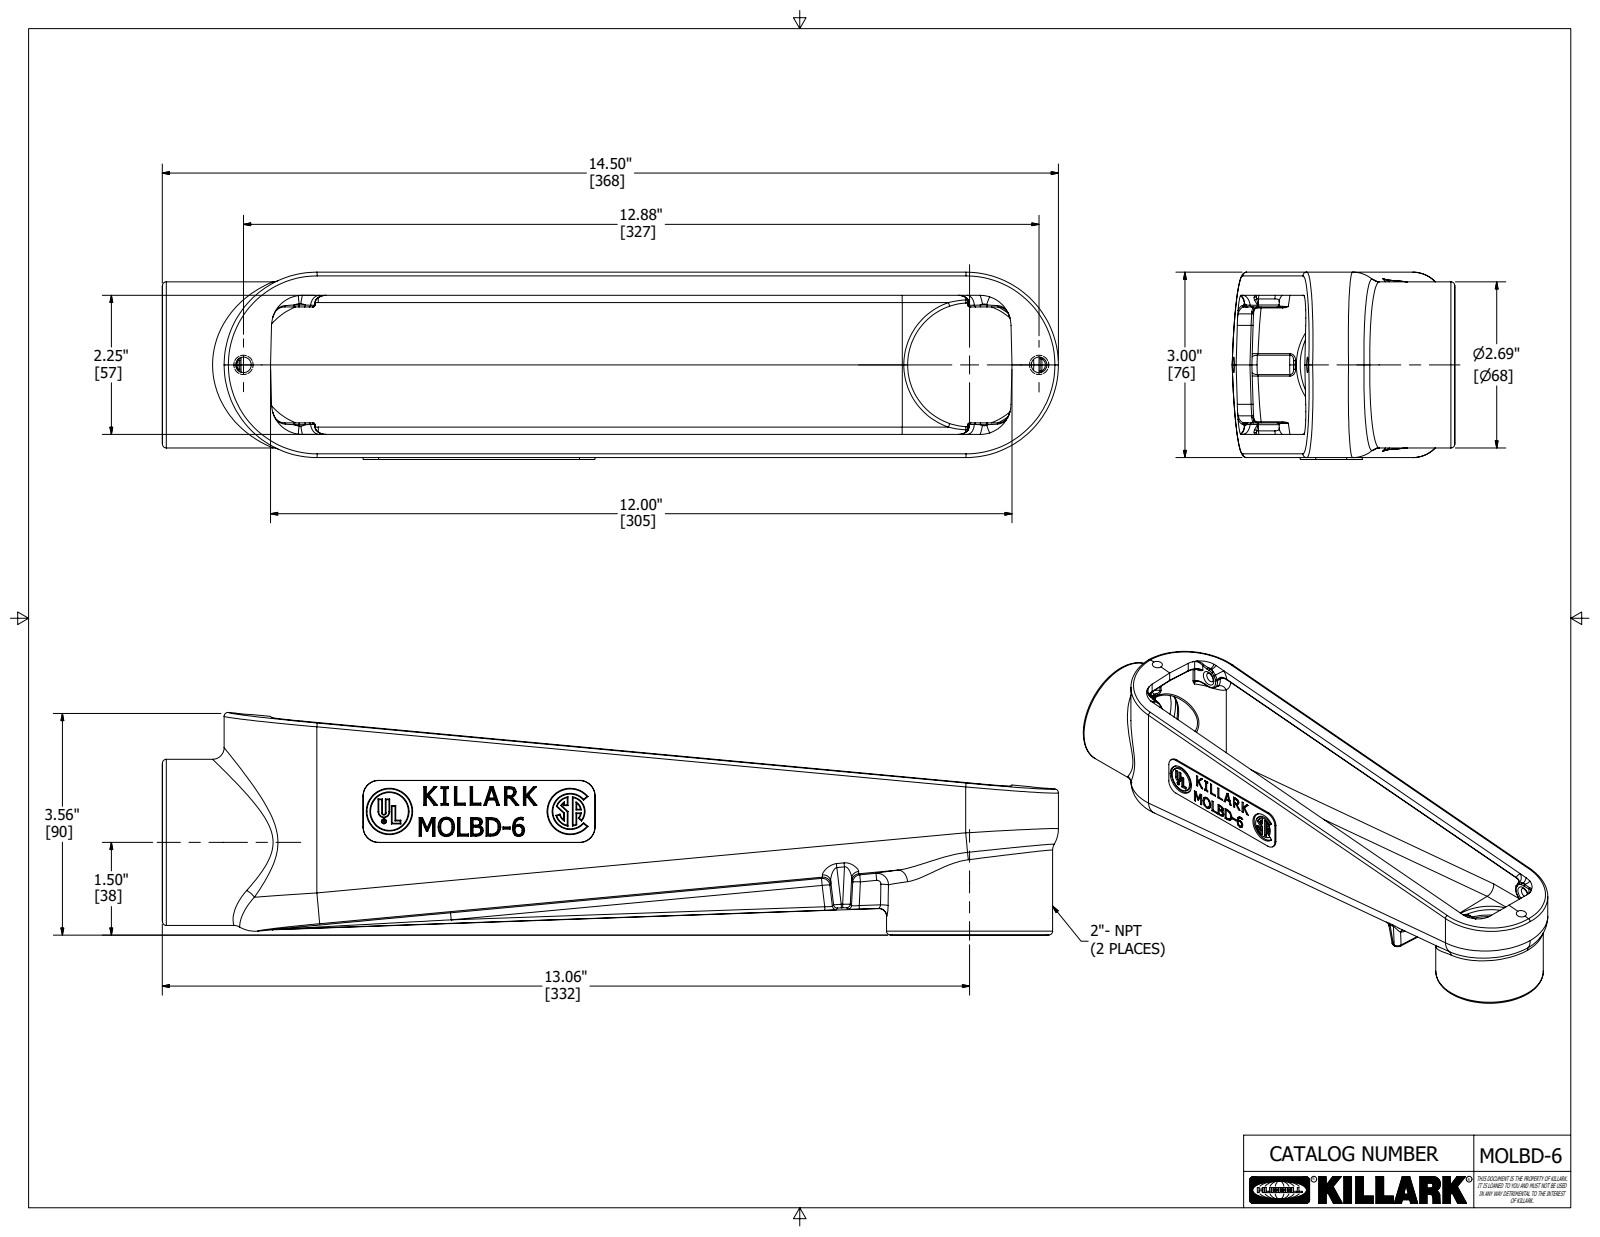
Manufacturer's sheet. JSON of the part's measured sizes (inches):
{"part_name": "21018-2", "step_written_by": "Autodesk Inventor 2020 (AUTOMOTIVE_DESIGN)", "units": "inches", "bodies": {"solids": 1, "faces": 757, "planar": 282, "cylindrical": 89, "other": 386}, "overall_size": [14.5, 3.602, 3.031], "volume_in3": 29.09, "surface_area_in2": 238.1, "round_holes": [[0.252, 2], [2.004, 2], [2.381, 2], [0.083, 1]], "round_bosses_or_shafts": [[2.688, 2], [0.07, 1]], "partial_cylinders_radius": [[0.125, 18], [0.031, 12], [0.062, 12], [0.031, 8], [0.187, 6], [0.5, 6], [0.25, 4], [0.171, 2]], "face_to_face_distances": [0.25, 2.75, 2.5, 3, 2.375, 0.281, 0.375, 2.625, 0.125, 0.031], "hole_center_spacings": [1.125, 11.75, 12.875]}
